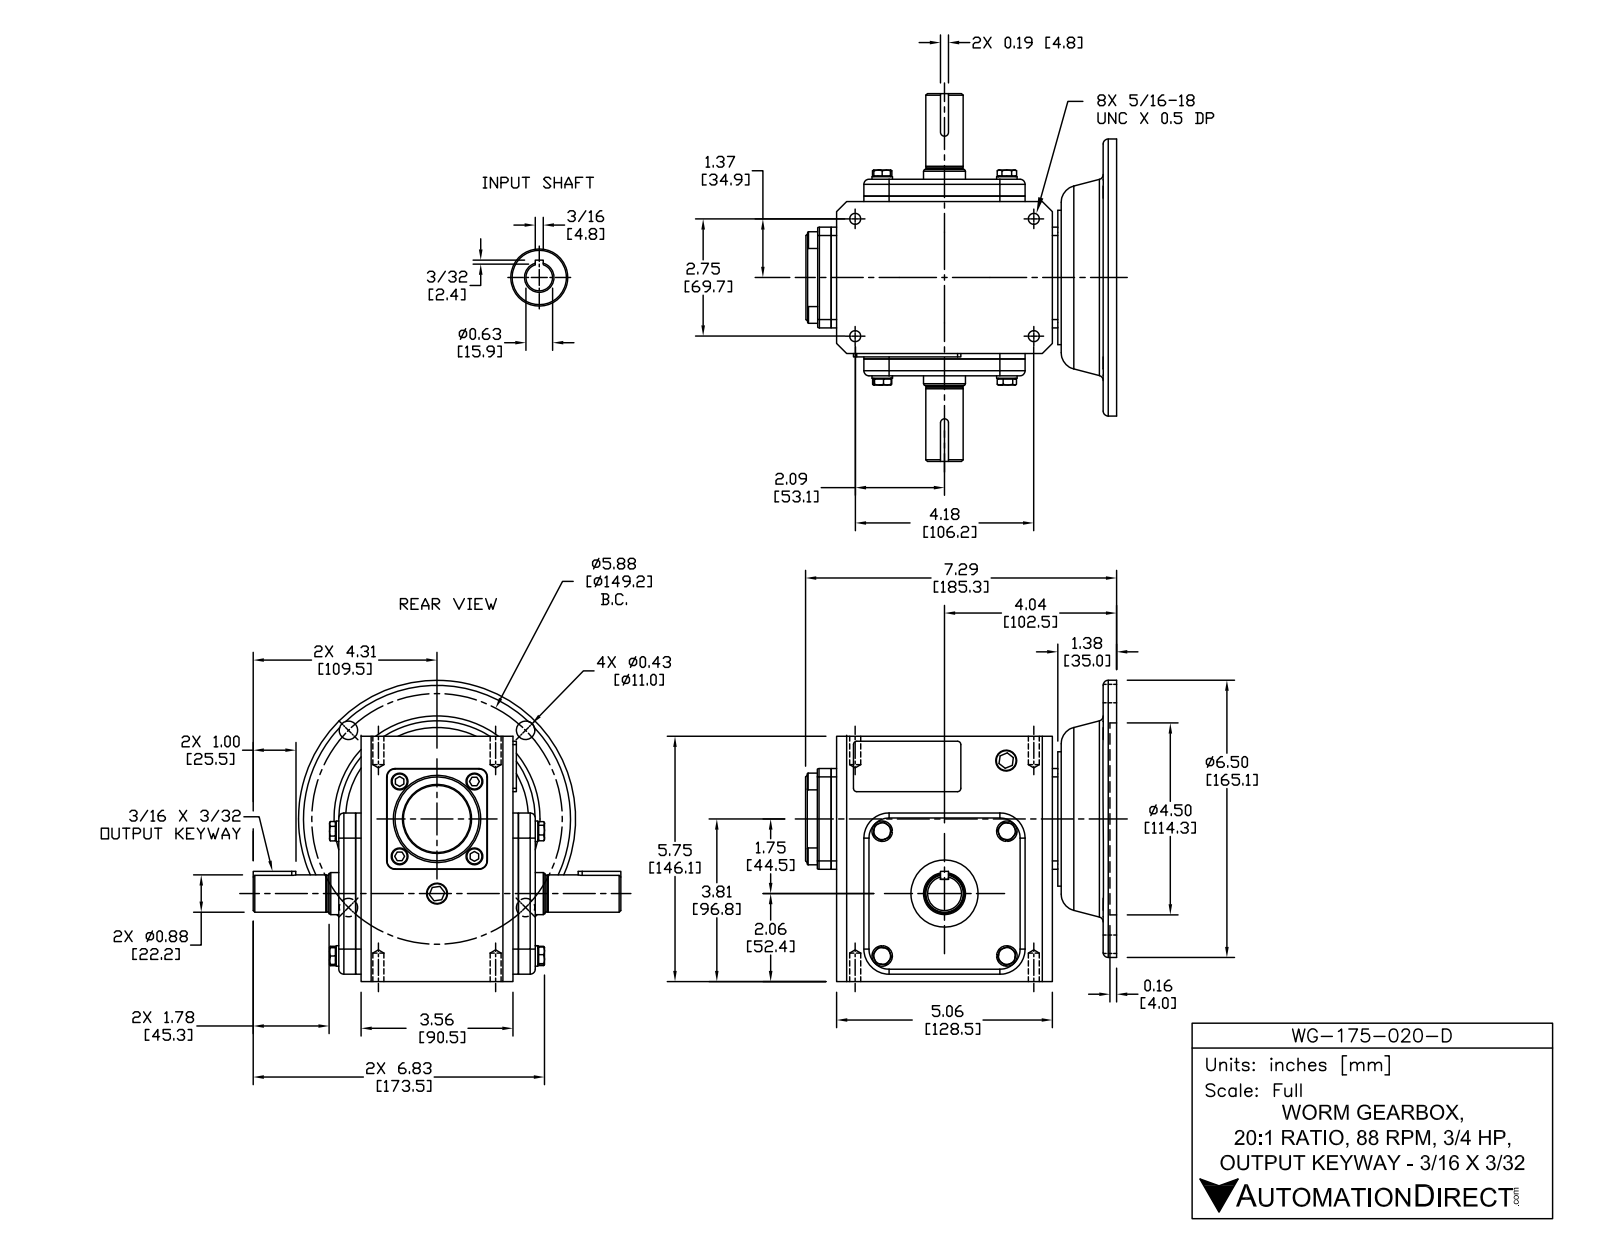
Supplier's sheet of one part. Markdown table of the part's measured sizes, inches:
| quantity | value |
| --- | --- |
| part name | WG-175-020-D |
| STEP written by | SolidWorks 2015 (CONFIG_CONTROL_DESIGN) |
| units | inches |
| bodies | 45 solids, 647 faces (324 planar, 186 cylindrical, 137 other) |
| overall size | 8.622 × 7.283 × 7.06 |
| volume | 133.1 in³ |
| surface area | 375.6 in² |
| round holes (diameter × count) | 0.257 × 4, 0.406 × 4, 0.512 × 1, 0.625 × 1, 0.984 × 1, 1.181 × 1, 1.457 × 1, 1.575 × 1, 3.543 × 1, 4.5 × 1 |
| round bosses / shafts (diameter × count) | 0.394 × 8, 0.48 × 4, 0.512 × 2, 6.496 × 1, 3.15 × 1, 2.047 × 1, 1.575 × 1, 0.875 × 1 |
| partial cylindrical surfaces (radius × count) | 0.079 × 8, 0.118 × 8, 0.197 × 4, 0.591 × 4, 0.02 × 2, 0.039 × 2, 0.094 × 2 |
| main face-to-face distances | 0.128, 3.819, 4.213, 0.394, 4.085, 3.691, 0.522, 0.315, 5.75, 6.693 |
| hole center spacings | 2.937, 4.154, 2.103, 2.75, 4.188, 4.354, 5.01, 5.875 |
